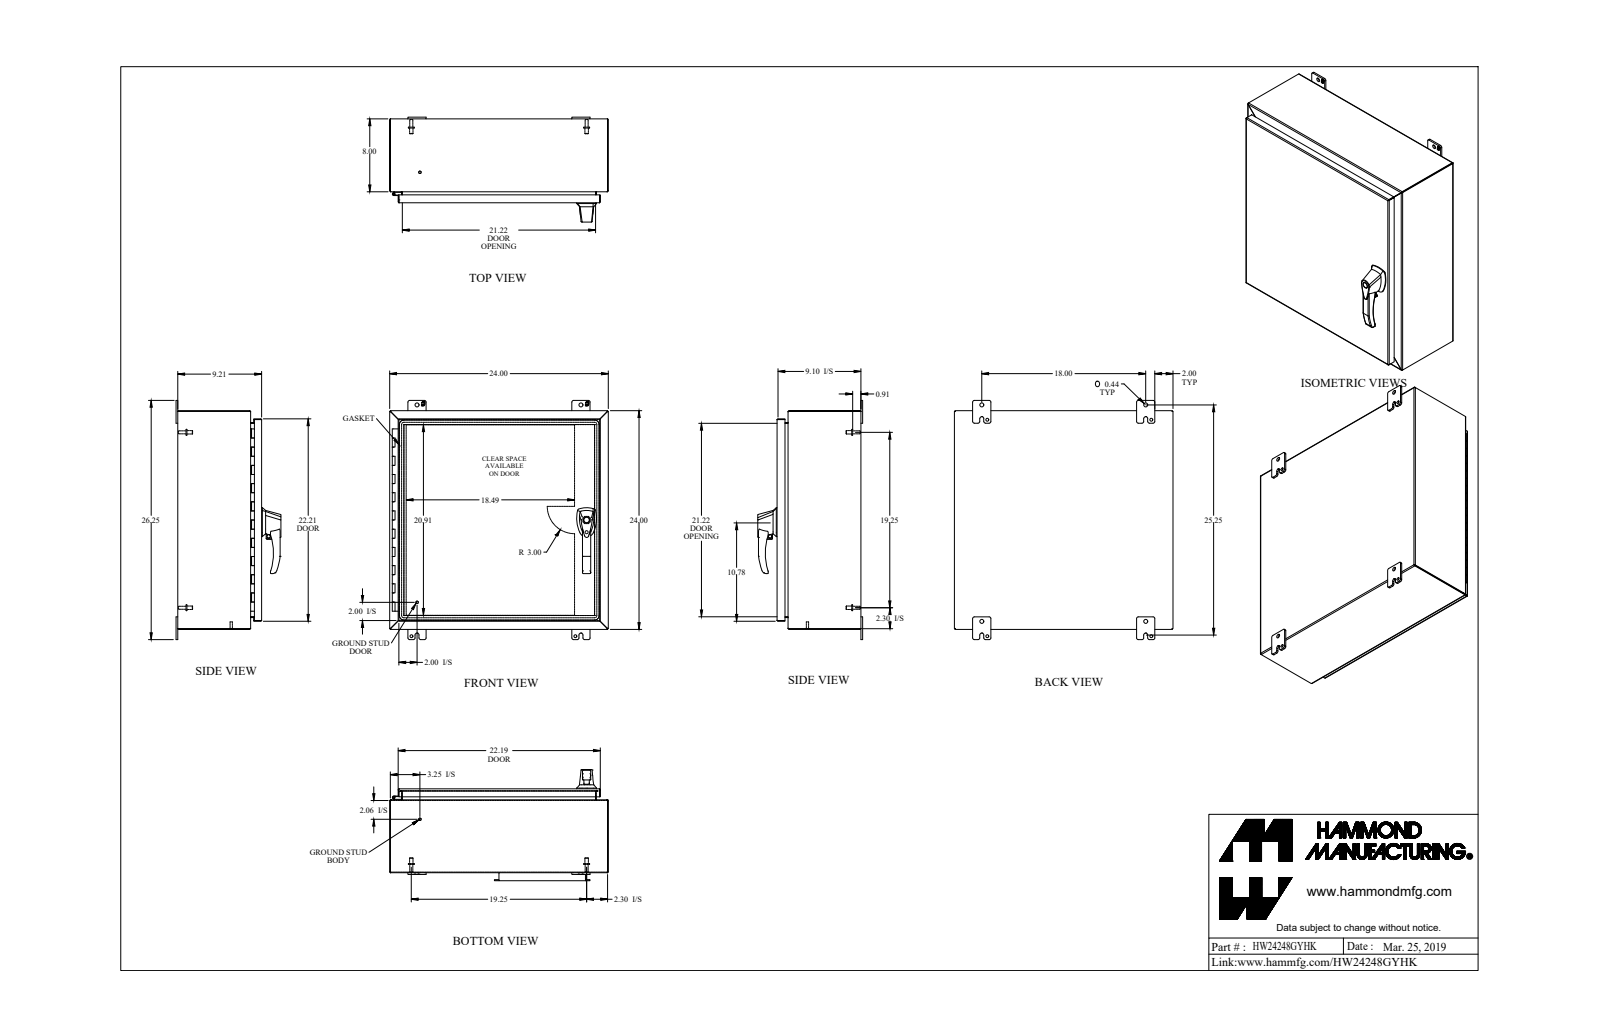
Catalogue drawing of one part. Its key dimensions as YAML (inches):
part_name: "HW24248GYHK"
step_written_by: "SolidWorks 2018 (AUTOMOTIVE_DESIGN)"
units: inches
bodies: {solids: 41, faces: 1406, planar: 691, cylindrical: 557, other: 158}
overall_size: [26.25, 24, 11.512]
volume: 189.1
surface_area: 4809
round_holes:
  - {diameter: 0.176, count: 6}
  - {diameter: 0.25, count: 4}
  - {diameter: 0.313, count: 4}
  - {diameter: 0.196, count: 3}
  - {diameter: 0.265, count: 3}
  - {diameter: 0.413, count: 3}
  - {diameter: 0.256, count: 2}
  - {diameter: 0.394, count: 2}
  - {diameter: 0.437, count: 2}
  - {diameter: 0.187, count: 1}
  - {diameter: 0.233, count: 1}
  - {diameter: 0.334, count: 1}
round_bosses_or_shafts:
  - {diameter: 0.375, count: 9}
  - {diameter: 0.25, count: 6}
  - {diameter: 0.156, count: 6}
  - {diameter: 0.65, count: 4}
  - {diameter: 0.33, count: 4}
  - {diameter: 1, count: 3}
  - {diameter: 0.63, count: 2}
  - {diameter: 0.51, count: 2}
partial_cylinders:
  - {radius: 0.25, count: 27}
  - {radius: 0.188, count: 24}
  - {radius: 0.036, count: 20}
  - {radius: 0.108, count: 20}
  - {radius: 0.06, count: 12}
  - {radius: 0.125, count: 9}
  - {radius: 0.045, count: 8}
  - {radius: 0.218, count: 8}
face_to_face_distances: [0.072, 23.928, 0.072, 9.138, 9.066, 9.21, 9.138, 23.856, 24, 7.928]
hole_center_spacings: [8.118, 8.119, 16.237, 1.111, 8.119, 18, 1.005, 1.005]
